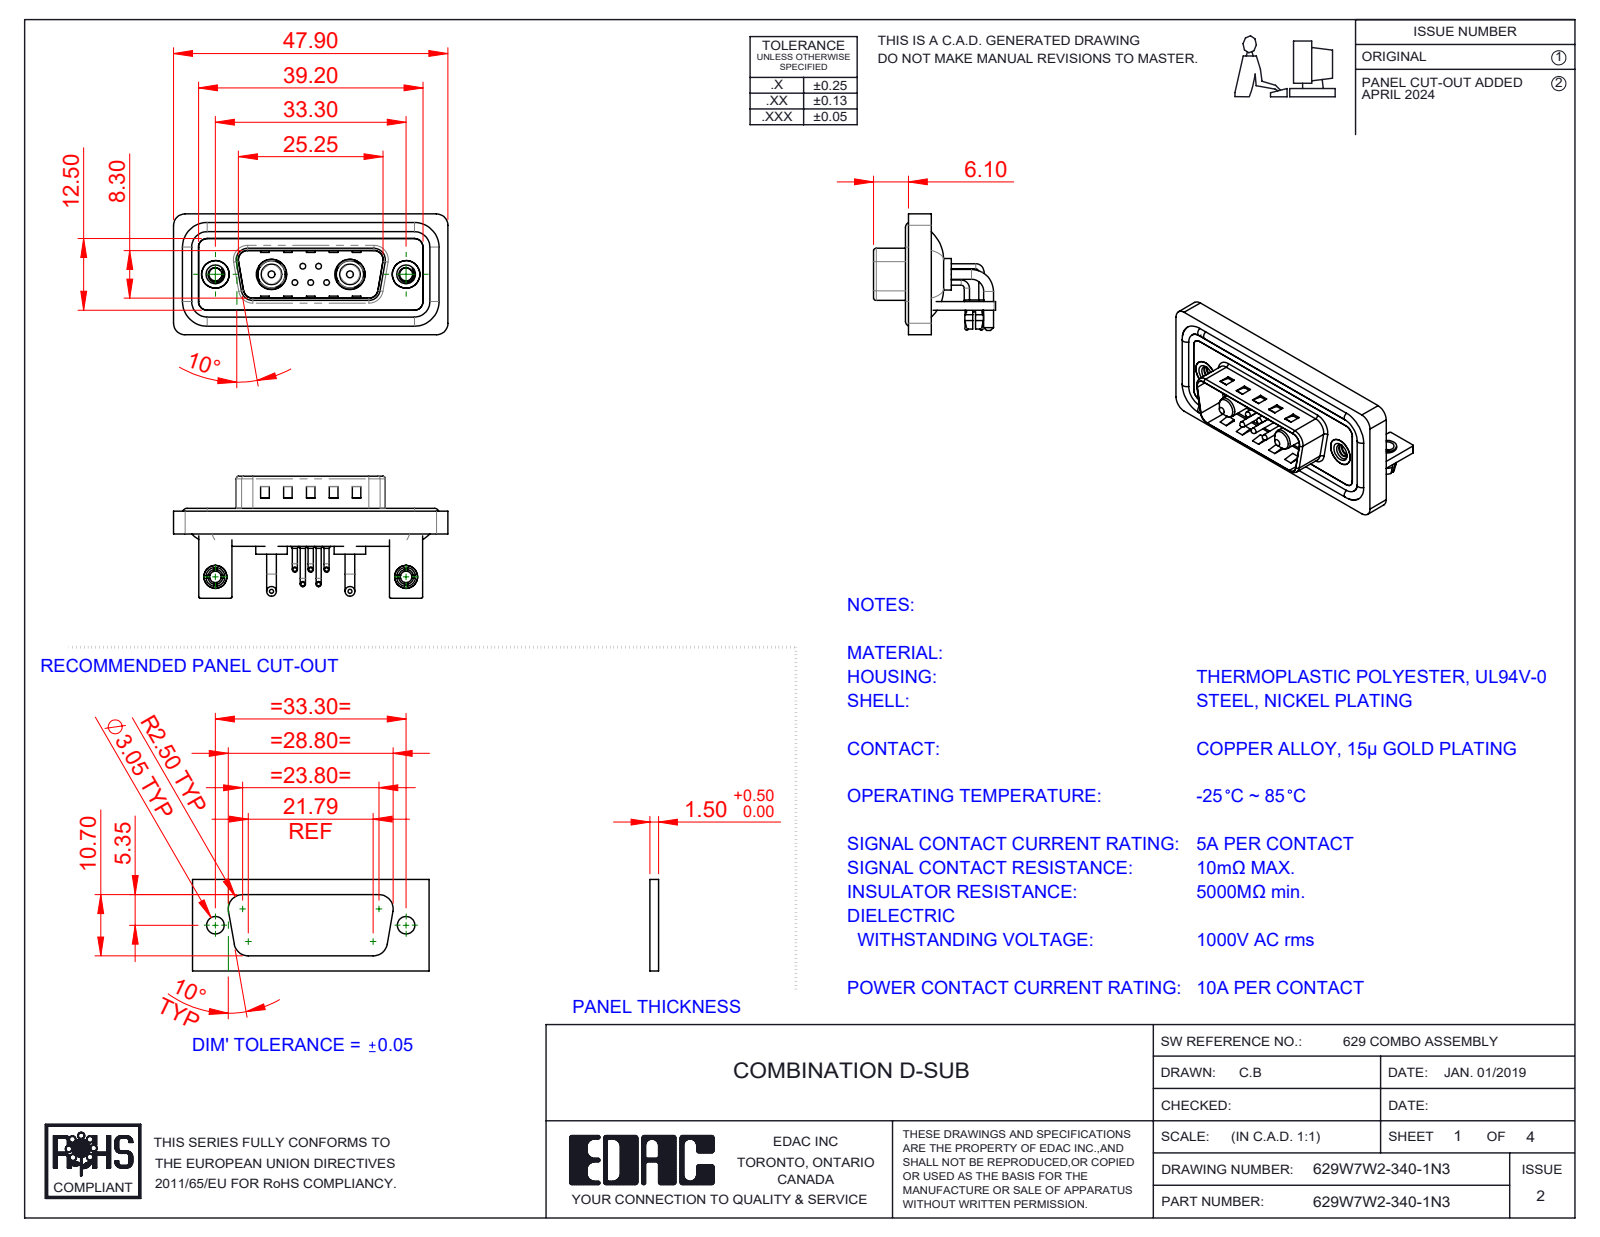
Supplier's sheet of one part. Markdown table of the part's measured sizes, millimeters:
| quantity | value |
| --- | --- |
| part name | 629Combo Shell Front_15 Contacts; 629Combo Housing_7W2; 629Combo Shell Rear_15 Contacts; 629Combo Waterproof Housing_15 Contacts (+7 more) |
| STEP written by | SolidWorks 2023 (CONFIG_CONTROL_DESIGN) |
| units | millimeters |
| bodies | 20 solids, 1215 faces (585 planar, 456 cylindrical, 174 other) |
| overall size | 47.9 × 21.3 × 21.1 |
| volume | 5 878 mm³ |
| surface area | 9 836 mm² |
| round holes (diameter × count) | 2 × 7, 0.75 × 5, 1.6 × 5, 2.26 × 2, 2.5 × 2, 3.2 × 2, 4 × 2, 4.8 × 2, 4.85 × 2, 5 × 2, 5.3 × 2 |
| round bosses / shafts (diameter × count) | 0.9 × 10, 1.5 × 5, 1 × 5, 0.65 × 5, 1.7 × 4, 1.6 × 4, 5.5 × 2, 5.2 × 2 |
| partial cylindrical surfaces (radius × count) | 2 × 21, 1.5 × 18, 0.25 × 16, 0.5 × 9, 1.6 × 8, 1.01 × 5, 0.6 × 4, 0.65 × 4 |
| main face-to-face distances | 0.4, 1.5, 0.8, 2.9, 2.1, 1.1, 1.6, 1.2, 3.7, 4.5 |
| hole center spacings | 3.16, 2.77, 9.8, 23.5, 33.3, 4.31, 4.33, 5.03 |
